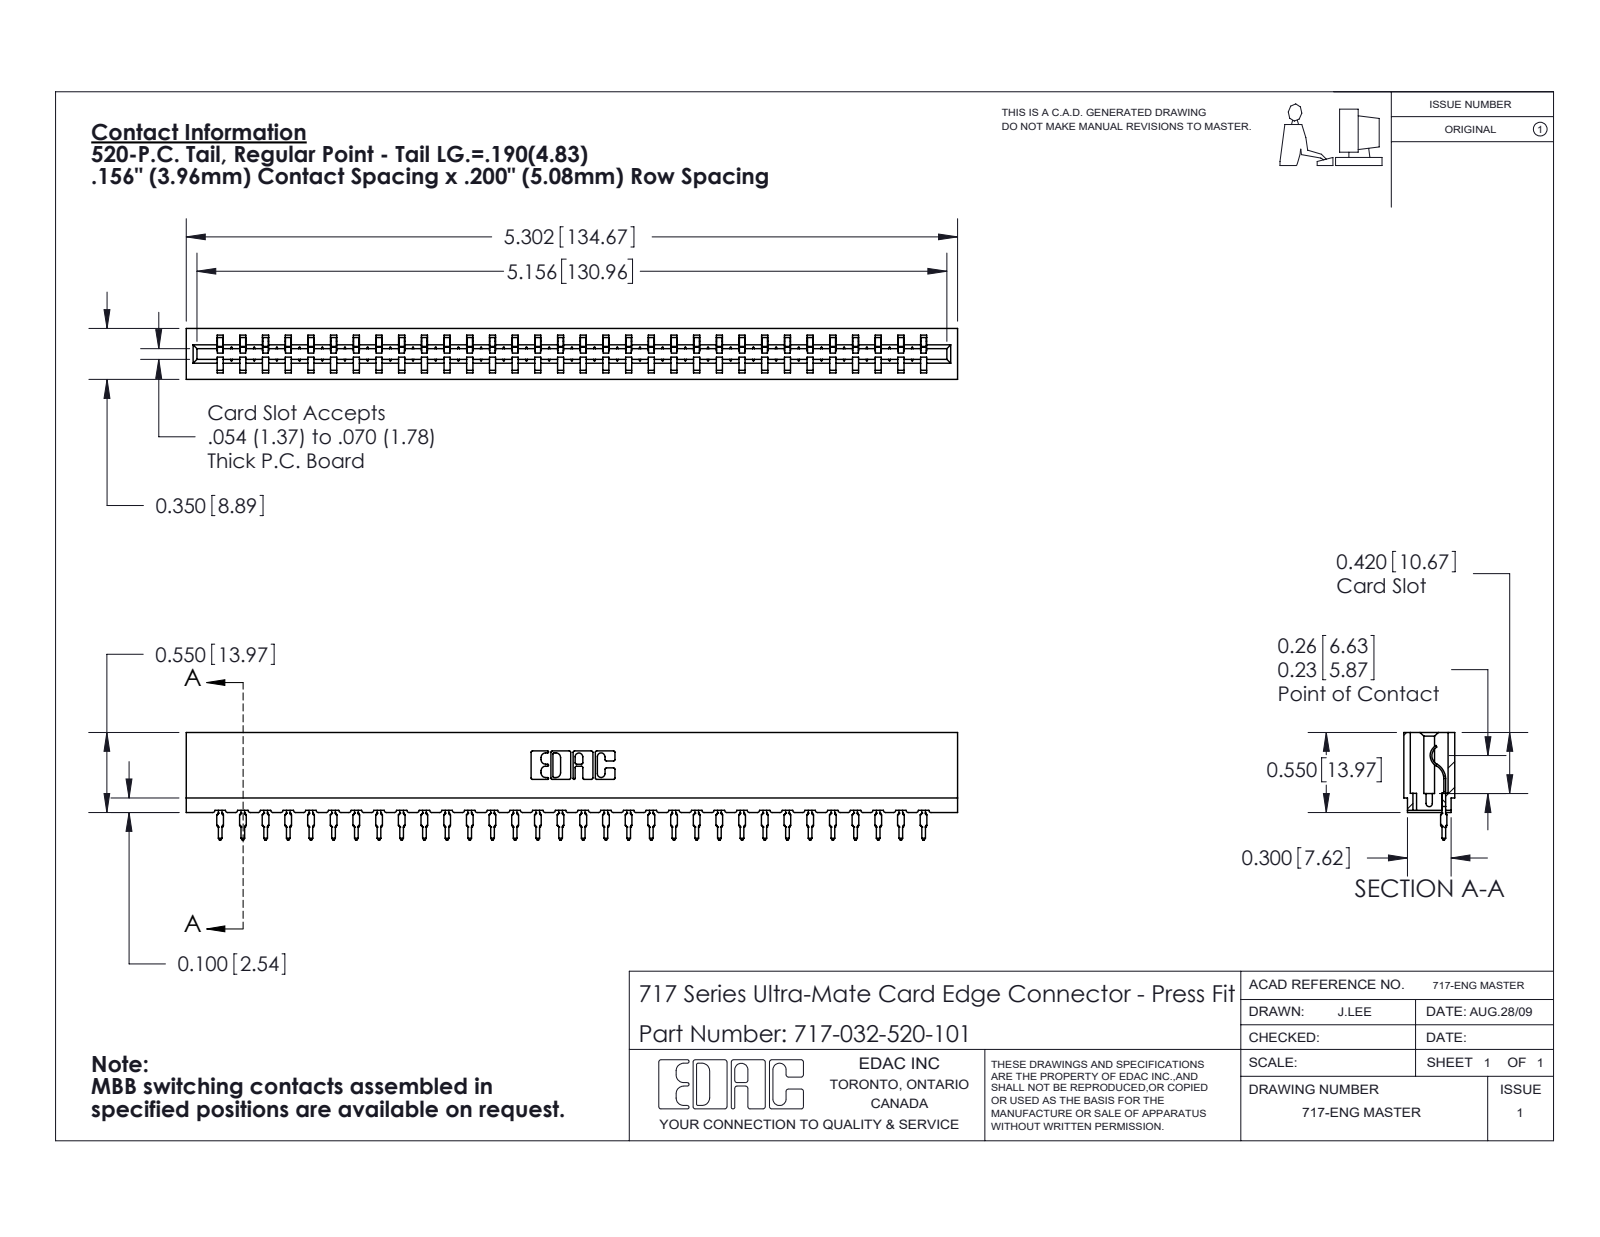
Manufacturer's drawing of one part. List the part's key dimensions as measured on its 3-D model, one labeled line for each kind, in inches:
Part name (STEP PRODUCT): 717-032-520-101; 717 Part_Insulator Option - 06; 745-292-001_520
STEP written by: SolidWorks 2020 (CONFIG_CONTROL_DESIGN)
Units: inches
Bodies: 33 solids, 3710 faces (2230 planar, 648 cylindrical, 832 other)
Overall size (bounding box): 5.302 × 0.739 × 0.35
Volume: 0.694 in³ · Surface area: 24.24 in²
Partial cylindrical surfaces — rounded edges, fillets, slot ends (radius × count): R0.015 ×64, R0.021 ×64, R0.01 ×22, R0.007 ×6, R0.031 ×6, R0.005 ×4, R0.011 ×4, R0.026 ×3
Main face-to-face distances: 0.212, 0.138, 0.35, 0.074, 0.045, 0.305, 0.093, 0.167, 0.025, 0.156
